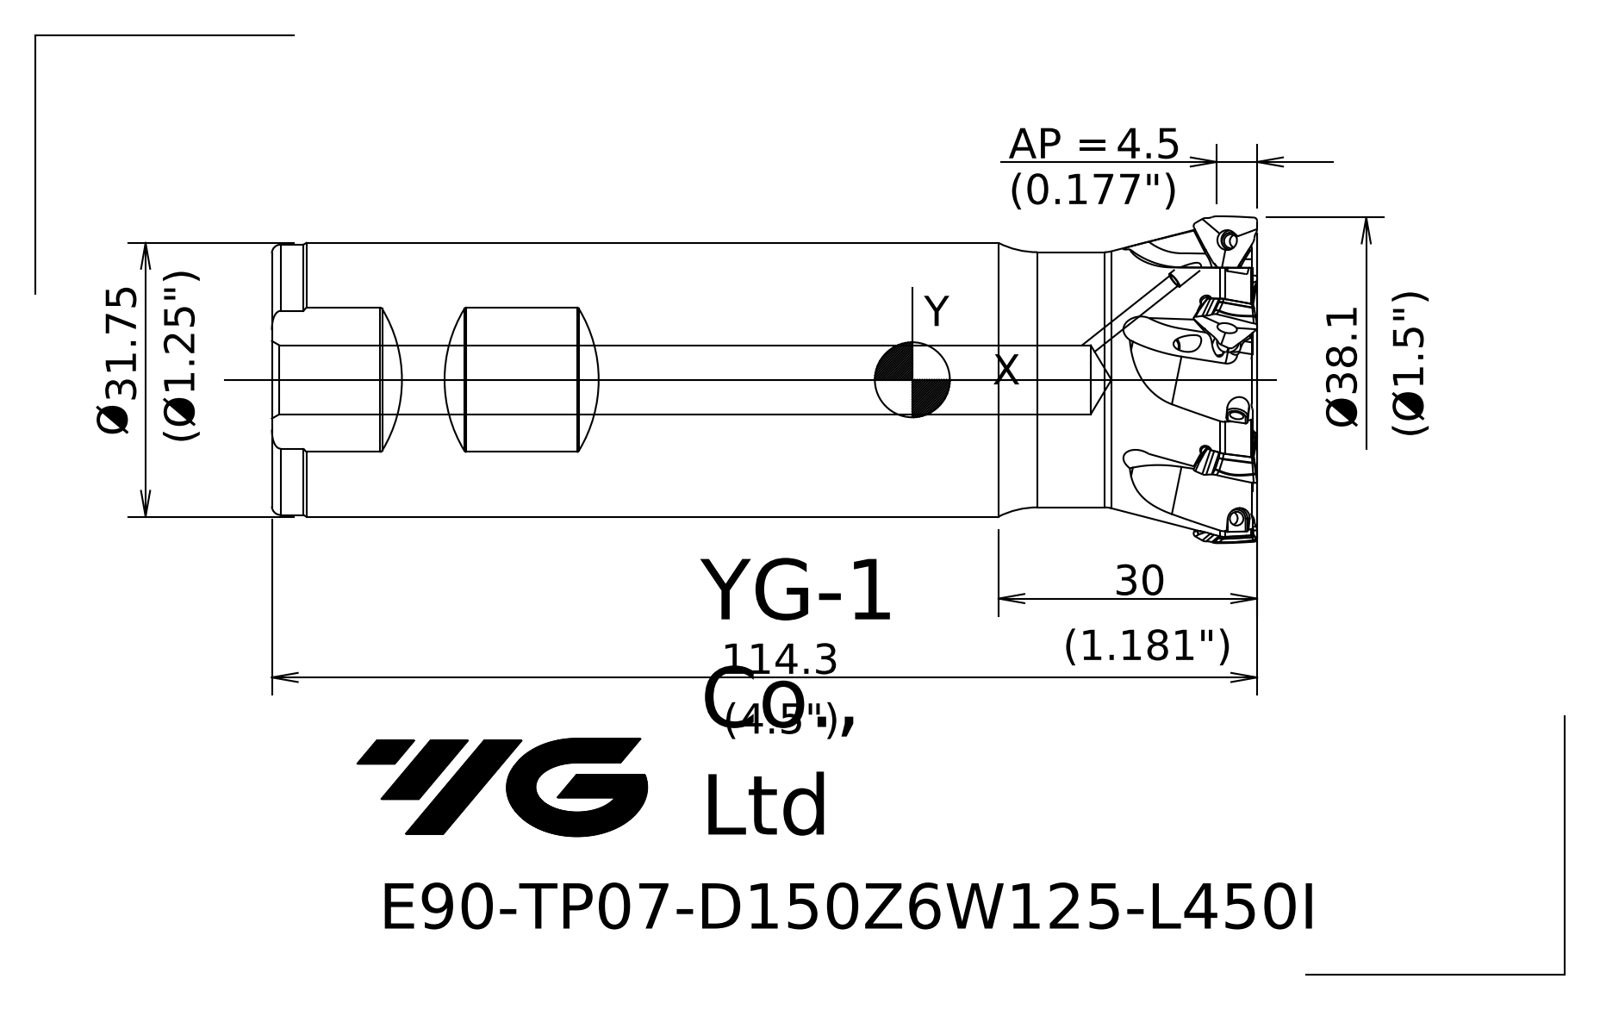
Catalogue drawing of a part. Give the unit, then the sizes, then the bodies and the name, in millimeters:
Units: millimetres
Overall size (bounding box): 114.3 × 38.16 × 38.16
Round holes (diameter × count): ⌀1.5 ×1, ⌀8 ×1
Round bosses / shafts (diameter × count): ⌀31.75 ×1, ⌀31.35 ×1, ⌀29.6 ×1
Partial cylindrical surfaces — rounded edges, fillets, slot ends (radius × count): R0.3 ×3
Main face-to-face distances: 113.65, 4.54, 109.11, 4.22, 0.32, 109.43, 4.37, 4.69, 113.8, 16.14
Volume: 88 514 mm³ · Surface area: 19 038 mm²
Bodies: 2 solids, 52 faces (10 planar, 8 cylindrical, 34 other)
Part name (STEP PRODUCT): 1022537C637A0f87
STEP written by: SIEMENS PLM Software NX 10.0 (AP203_CONFIGURATION_CONTROLLED_3D_DESIGN_OF_MECHANICAL_PARTS_AND_ASSEMBLIES_MIM_LF)
